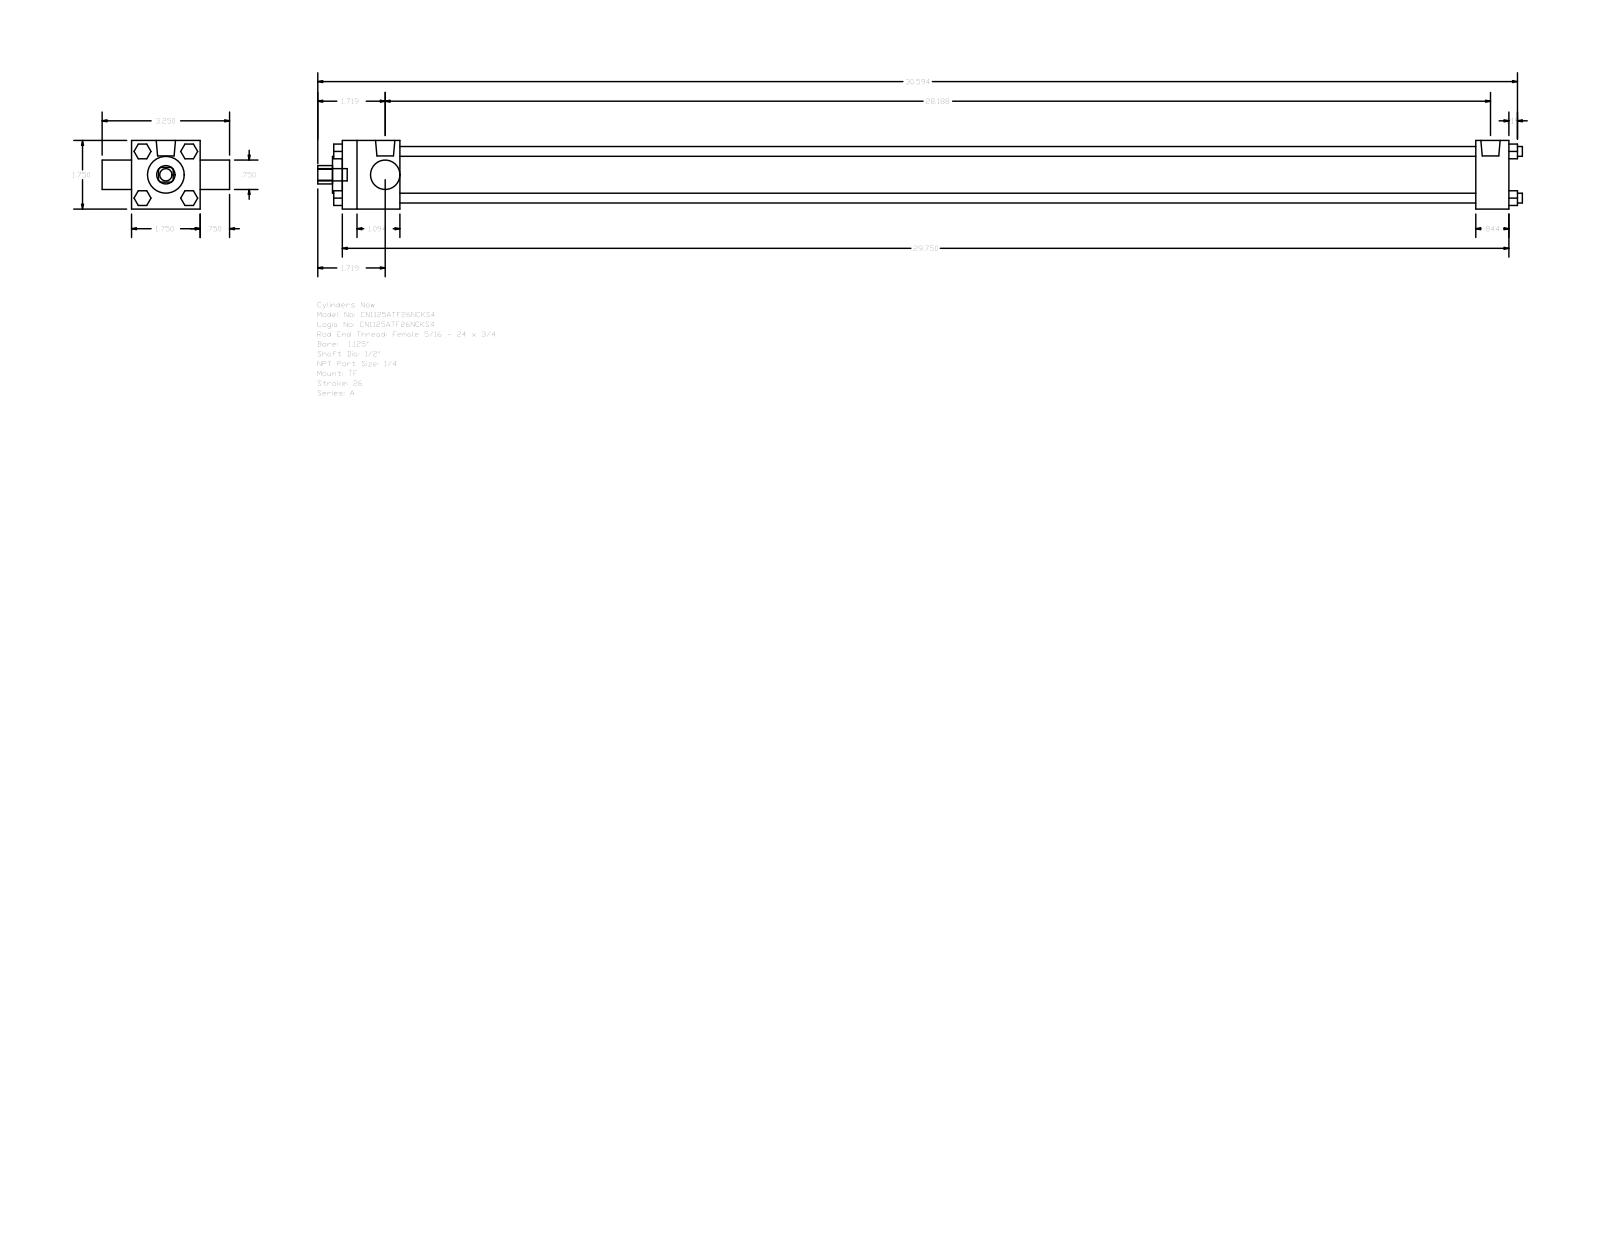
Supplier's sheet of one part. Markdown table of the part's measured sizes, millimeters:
| quantity | value |
| --- | --- |
| part name | A_TF__0112_0.5 |
| STEP written by | GSSL Pune (CONFIG_CONTROL_DESIGN) |
| units | millimeters |
| bodies | 0 solids, 120 faces (92 planar, 28 cylindrical, 0 other) |
| overall size | 780.26 × 82.55 × 44.45 |
| round holes (diameter × count) | 12.7 × 1, 19.05 × 1, 23.81 × 1, 31.88 × 1 |
| round bosses / shafts (diameter × count) | 6.35 × 4, 5.56 × 3, 12.49 × 2, 7.94 × 1 |
| partial cylindrical surfaces (radius × count) | 5.94 × 1 |
| main face-to-face distances | 44.46, 755.64, 734.21, 21.43, 37.3, 696.91, 718.34, 19.04, 63.5, 9.53 |
